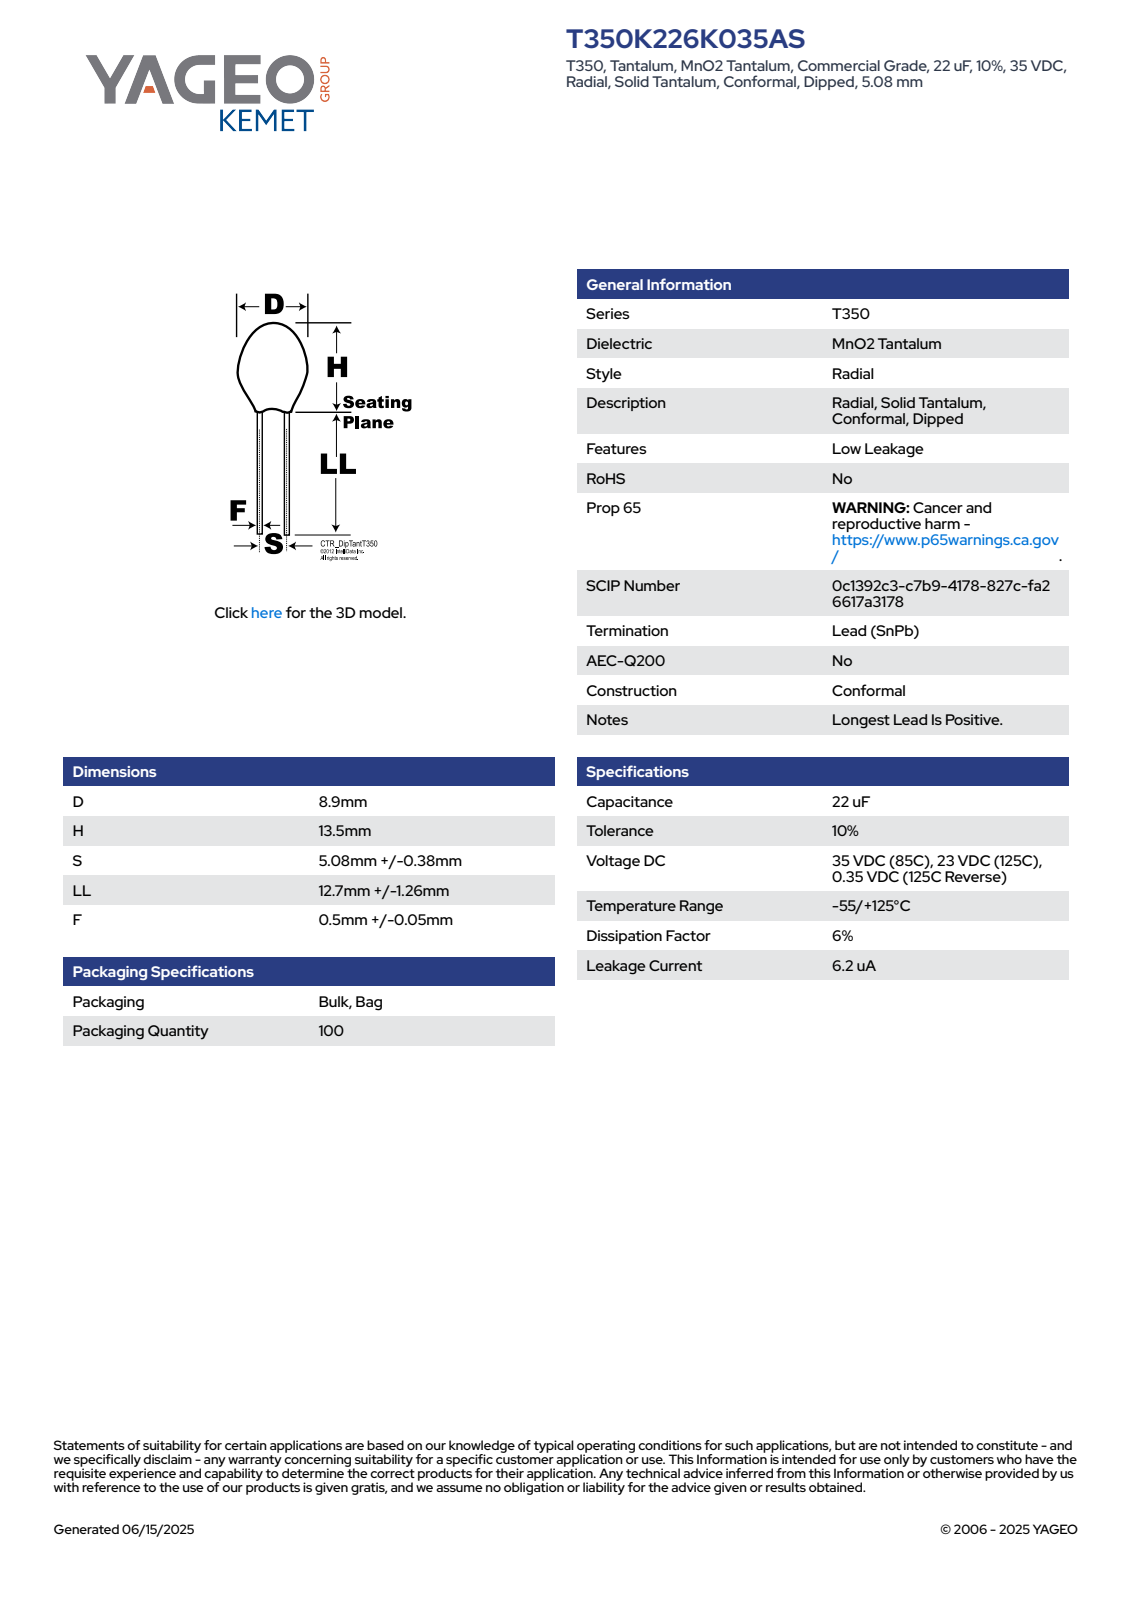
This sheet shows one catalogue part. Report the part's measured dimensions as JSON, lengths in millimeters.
{"part_name": "CTR_T350_D8.9H13.5S5.08LL13.96F0.55", "step_written_by": "SolidWorks 2014 (AUTOMOTIVE_DESIGN)", "units": "millimeters", "bodies": {"solids": 1, "faces": 73, "planar": 26, "cylindrical": 10, "other": 37}, "overall_size": [27.46, 8.9, 8.9], "volume_mm3": 683, "surface_area_mm2": 446, "round_bosses_or_shafts": [[0.55, 2], [8.9, 1]], "partial_cylinders_radius": [[4.44, 1]], "face_to_face_distances": [13.5, 13.96, 27.46, 21.38, 7.42, 6.08, 20.17, 6.21, 1.21, 7.29]}
